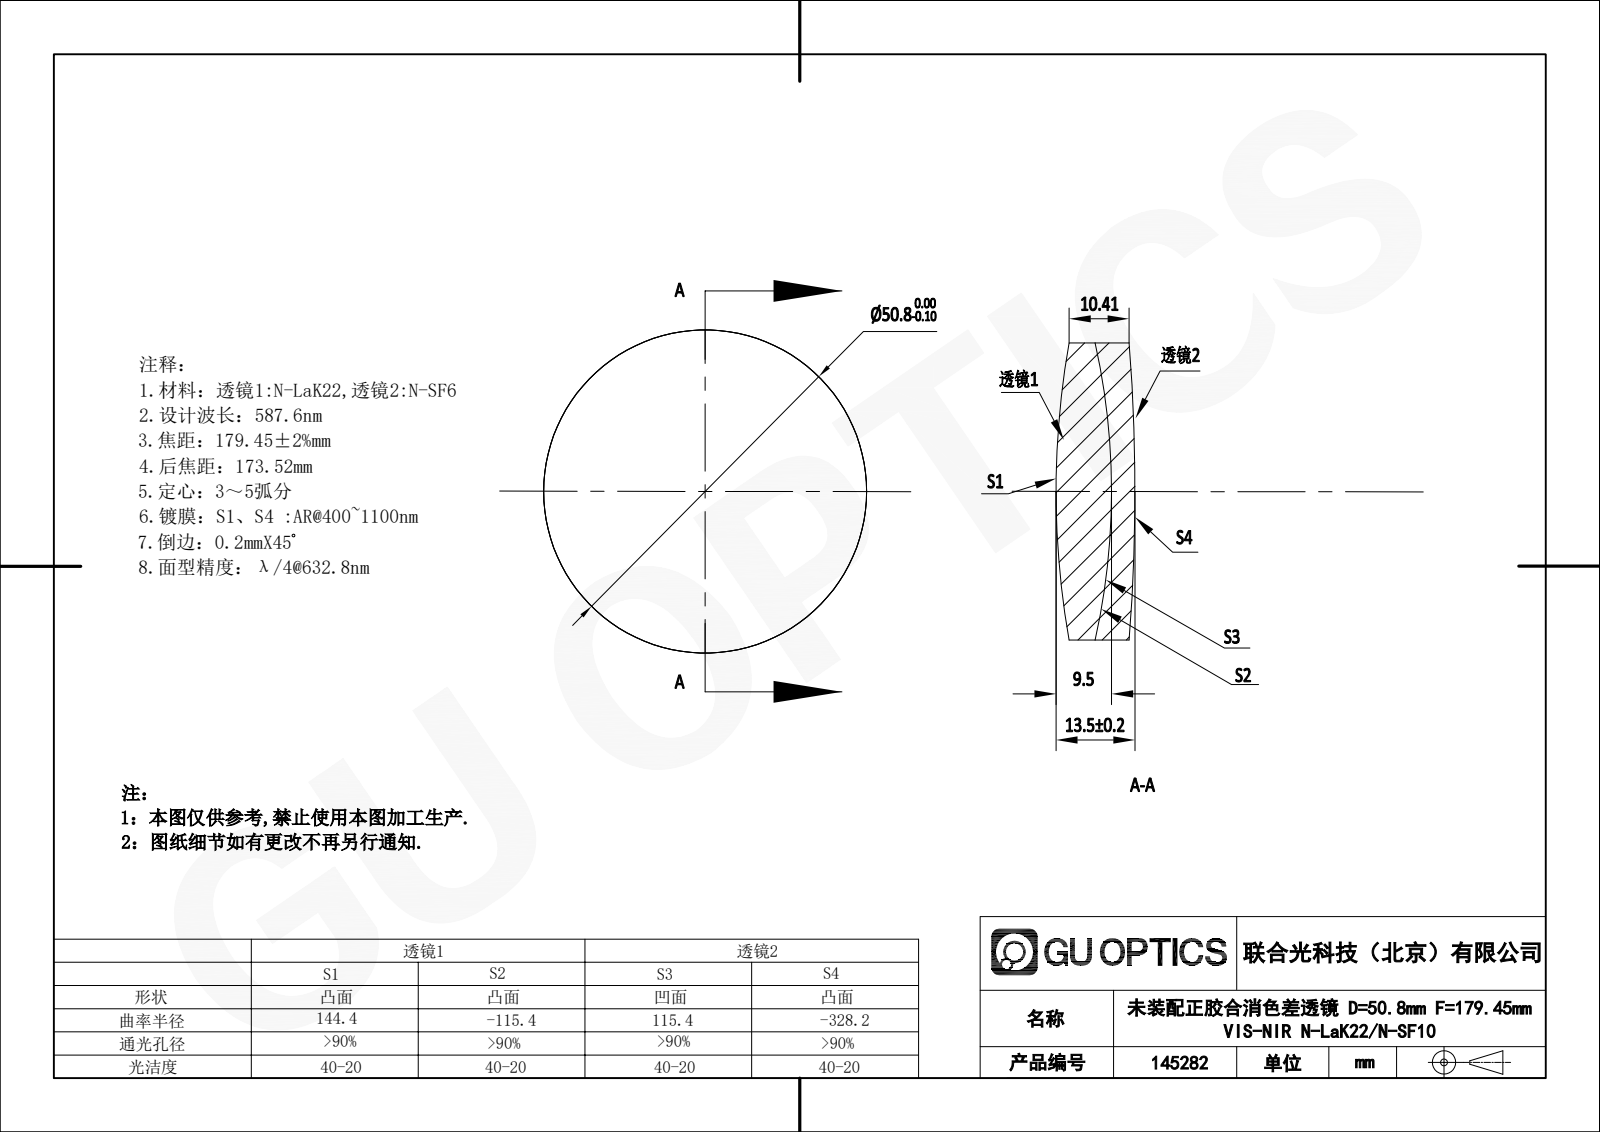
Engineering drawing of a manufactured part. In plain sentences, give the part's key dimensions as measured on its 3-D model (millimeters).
The part is named "145282". Its 3-D file was written by "SolidWorks 2020 (CONFIG_CONTROL_DESIGN)". It is 2 solids with 12 faces: 0 planar, 4 cylindrical and 8 other. Overall it measures 50.8 by 50.8 by 13.5 millimeters. Its volume is 24 089 cubic millimeters and its surface area 9 815 square millimeters. Round bosses or shafts: 1 of diameter 50.8.
